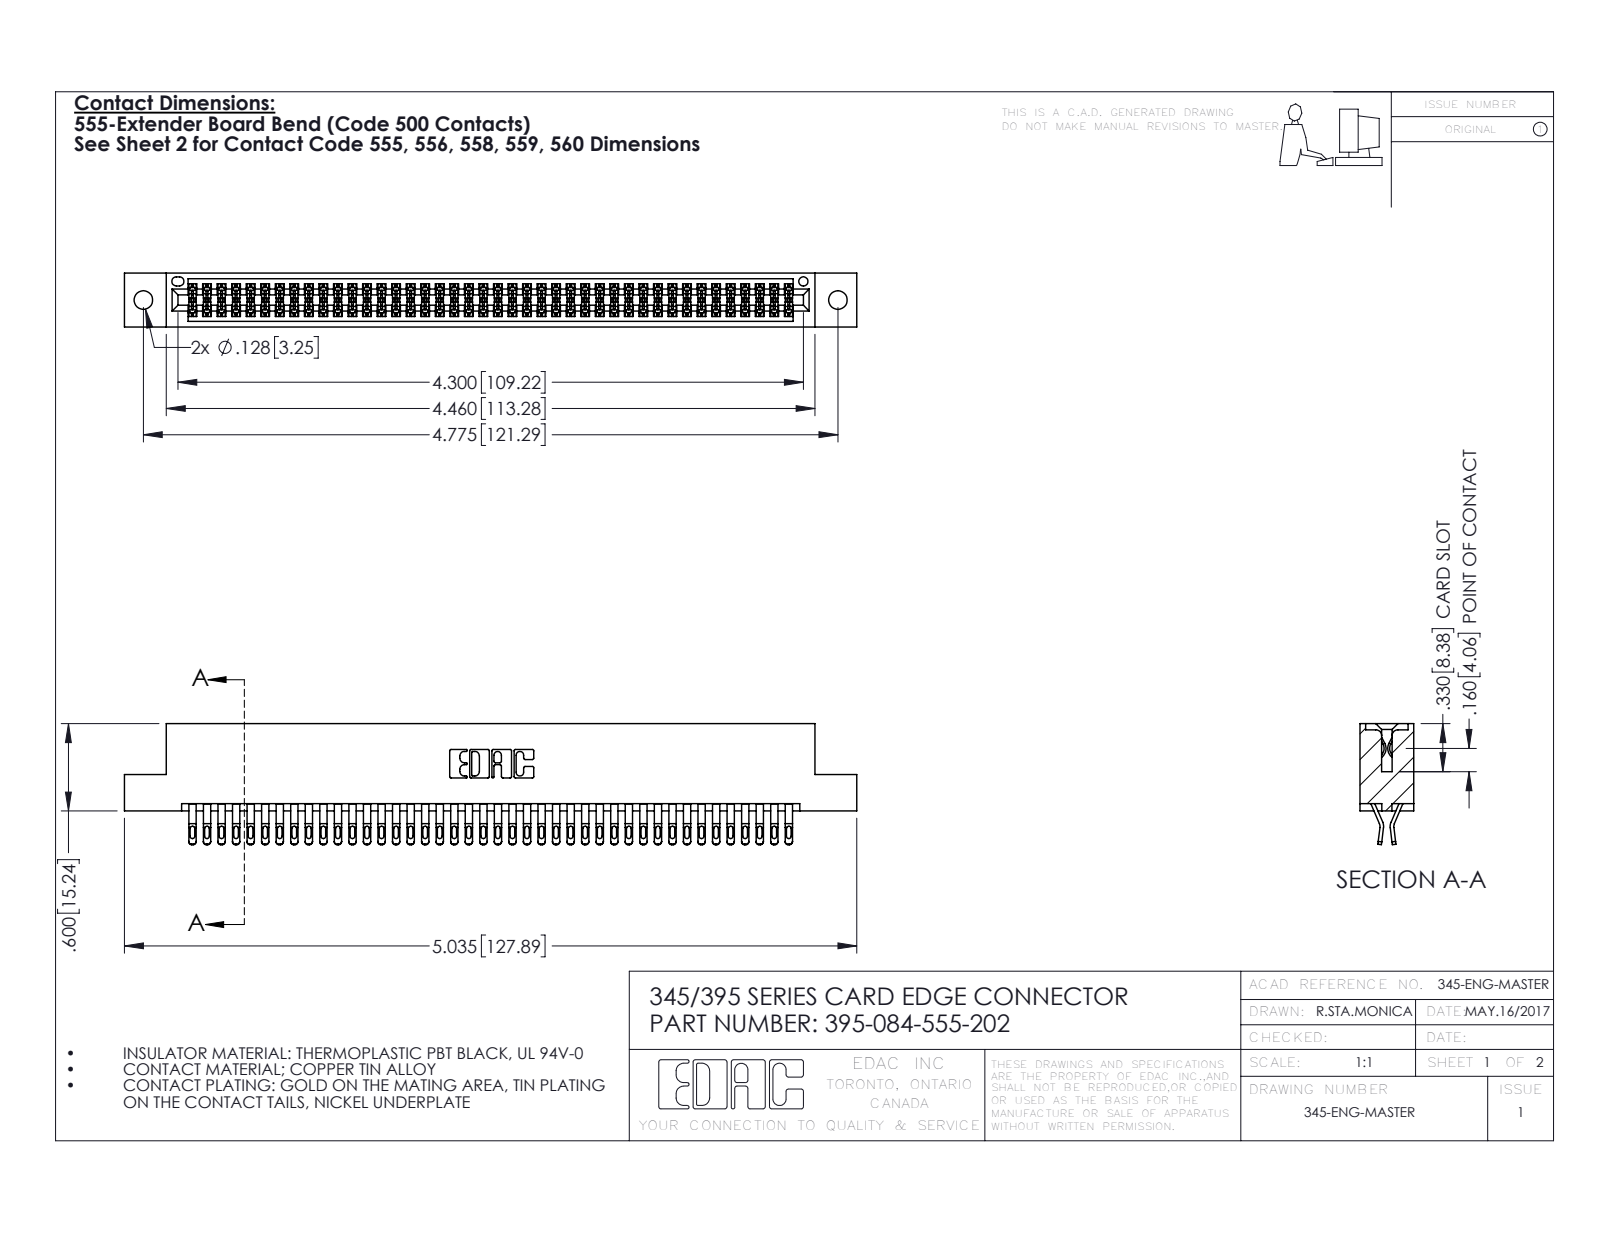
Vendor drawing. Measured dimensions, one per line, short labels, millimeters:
name: 345 Part_Flush Mounting Lugs - 0.128 Dia; 345-292-001_555 Tail; 395-084-555-202
written by: SolidWorks 2016 (CONFIG_CONTROL_DESIGN)
unit: mm
bodies: 85 solids, 4830 faces (2684 planar, 2146 cylindrical, 0 other)
size: 127.9 × 21.1 × 9.4
volume: 12 600 mm³; area: 19 250 mm²
holes: 2× ⌀3.3, 1× ⌀1.6
rounds: 210× R0.4, 168× R0.5, 126× R0.2, 22× R0.3, 6× R0.2, 6× R0.8, 3× R0.7, 2× R0.3
face distances: 7.6, 1.8, 5.1, 0.6, 9.4, 2.5, 6.9, 5.7, 4.4, 3.8
hole spacings: 6.9, 115.3, 121.3
